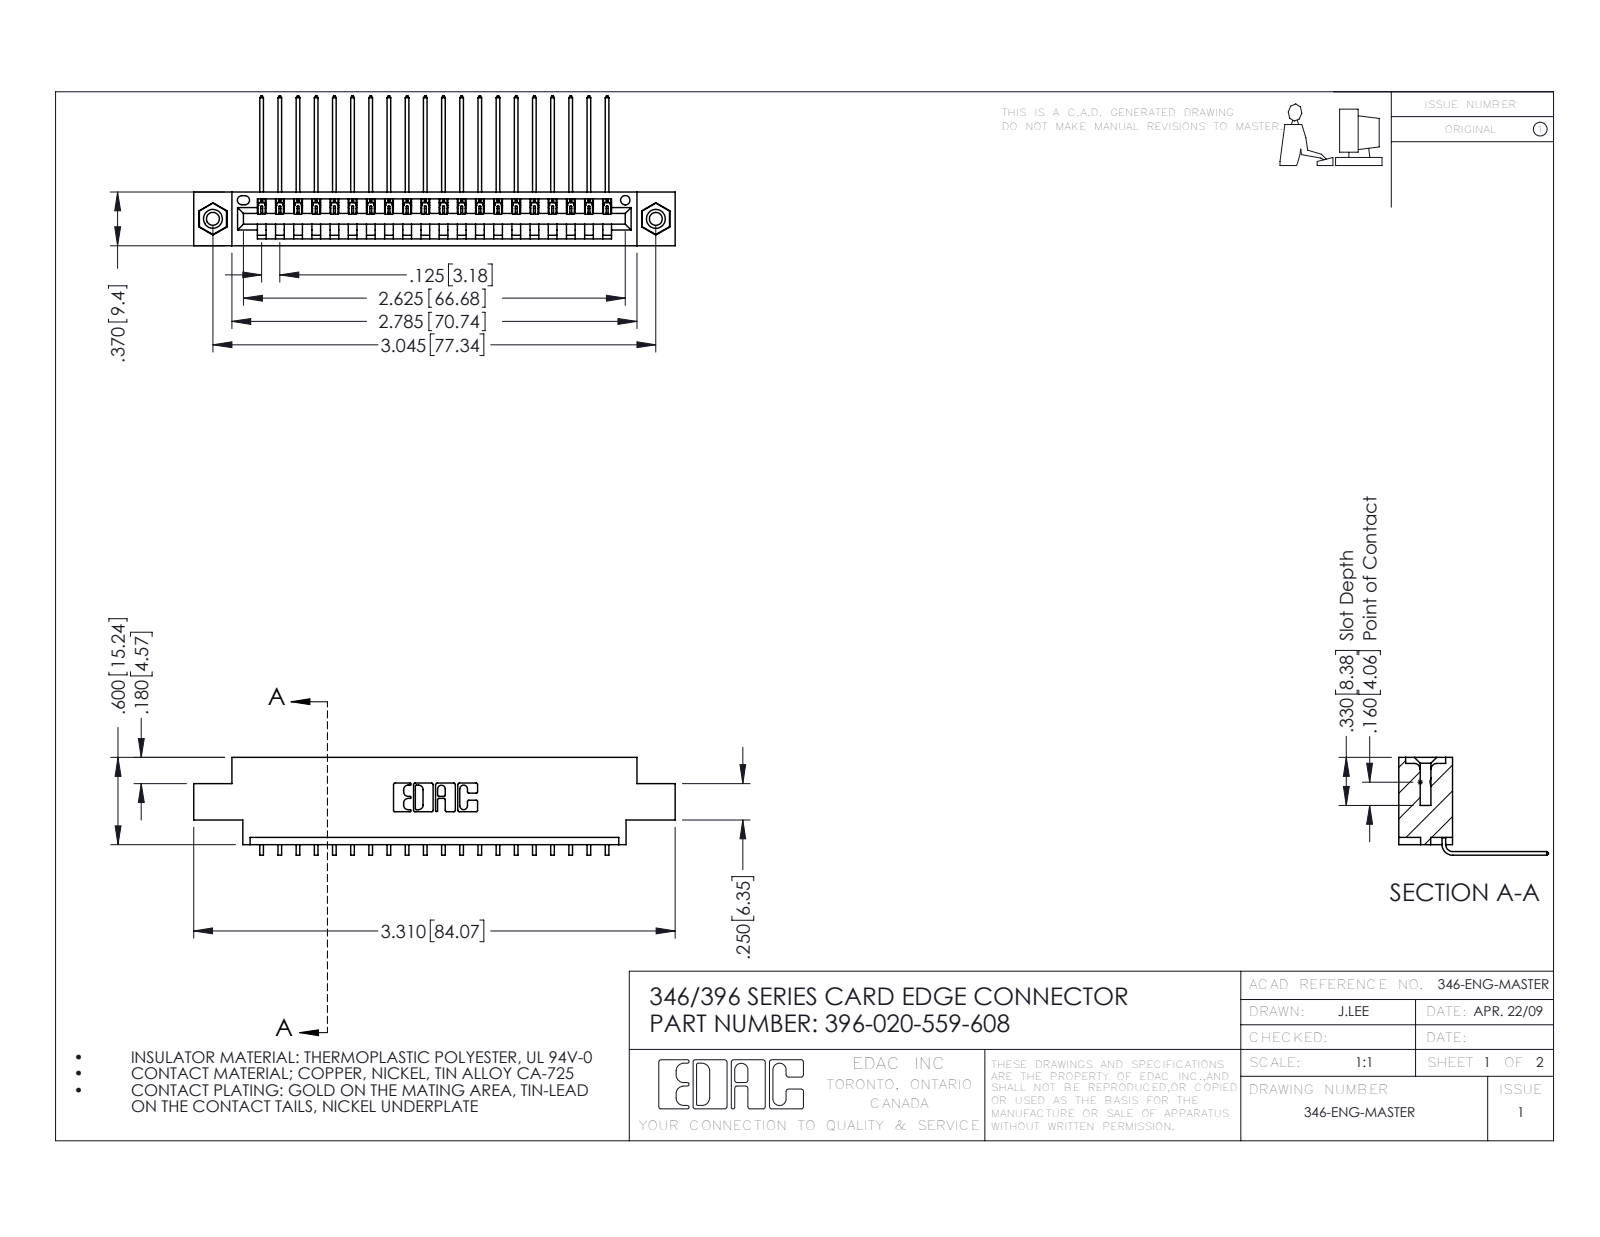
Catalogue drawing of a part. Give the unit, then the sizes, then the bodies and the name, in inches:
Units: inches
Overall size (bounding box): 3.31 × 1.03 × 0.673
Round holes (diameter × count): ⌀0.089 ×2, ⌀0.125 ×2, ⌀0.156 ×2, ⌀0.064 ×1
Round bosses / shafts (diameter × count): ⌀0.155 ×2
Partial cylindrical surfaces — rounded edges, fillets, slot ends (radius × count): R0.006 ×40, R0.01 ×22, R0.007 ×6, R0.031 ×6, R0.026 ×3, R0.031 ×2, R0.04 ×2, R0.014 ×1
Main face-to-face distances: 0.048, 0.322, 0.37, 0.25, 0.025, 0.072, 0.222, 0.148, 0.1, 0.174
Hole centre spacings: 0.246, 2.837, 3.045
Volume: 0.476 in³ · Surface area: 15.64 in²
Bodies: 23 solids, 1386 faces (952 planar, 418 cylindrical, 16 other)
Part name (STEP PRODUCT): 396-020-559-608; 345-250-001_345-250-003-102; 346 Part_0.170 Offset - 0.156 Dia-TI; 345-292-001_558 559 Tail - 1
STEP written by: SolidWorks 2016 (CONFIG_CONTROL_DESIGN)
